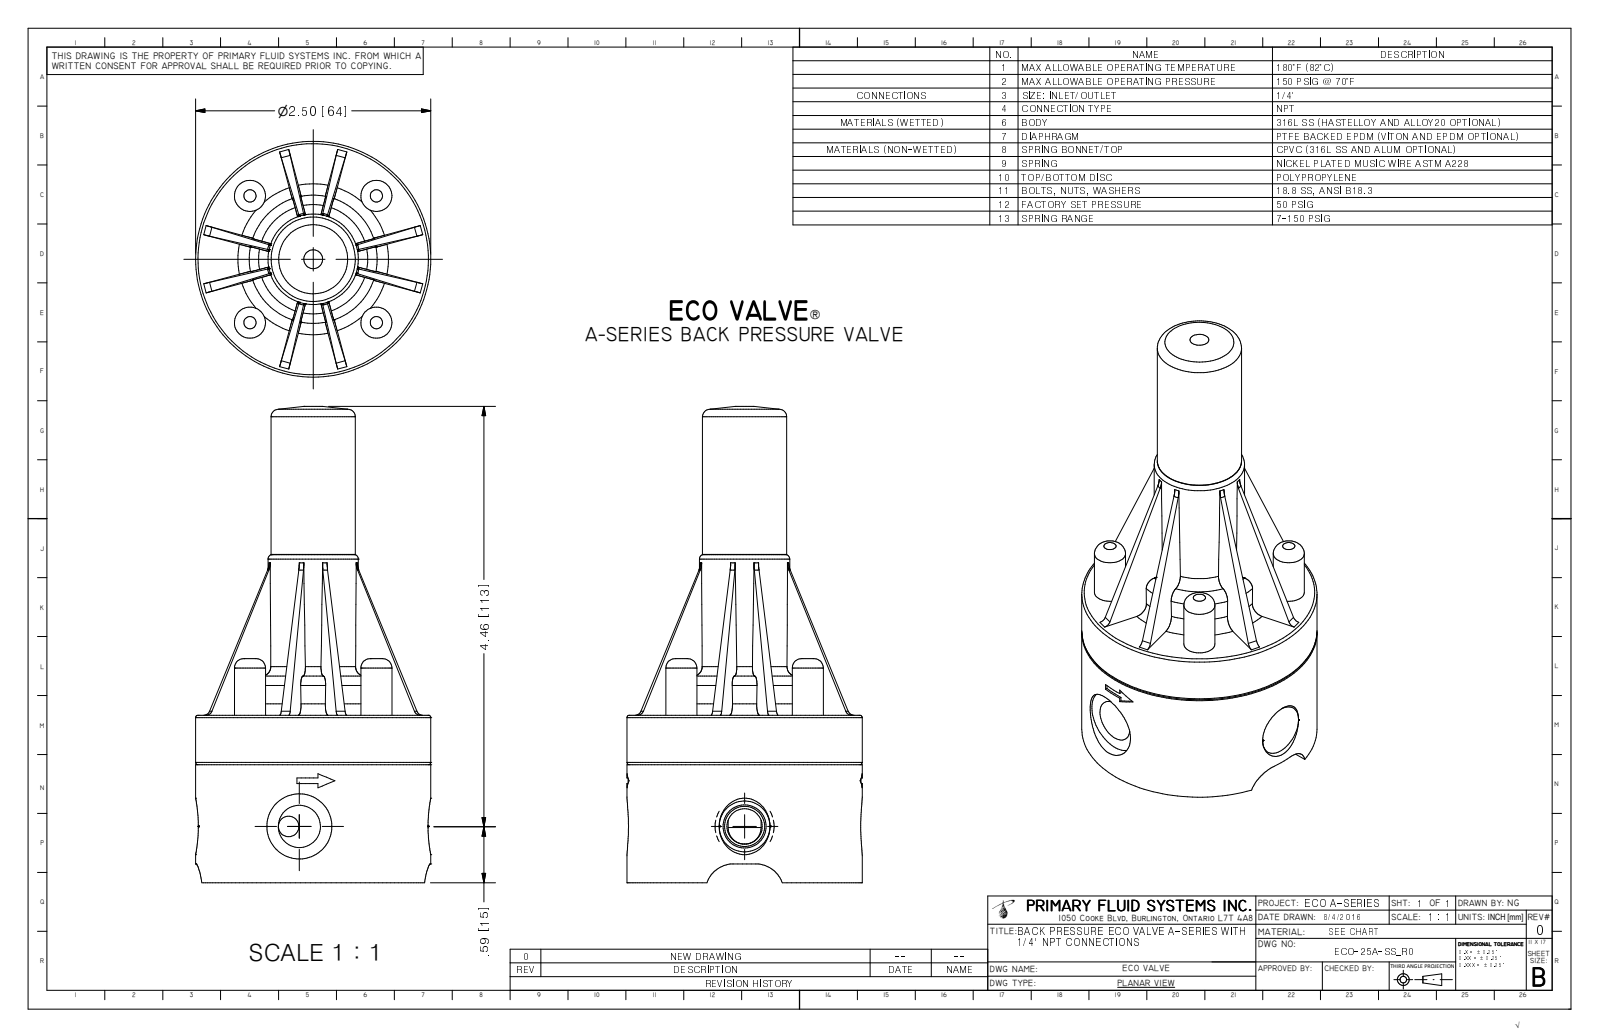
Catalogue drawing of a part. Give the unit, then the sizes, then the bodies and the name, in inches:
Units: inches
Overall size (bounding box): 5.051 × 2.5 × 2.5
Round holes (diameter × count): ⌀0.23 ×4, ⌀0.257 ×4, ⌀0.4 ×4, ⌀0.218 ×1, ⌀0.448 ×1, ⌀0.691 ×1
Round bosses / shafts (diameter × count): ⌀0.33 ×4, ⌀0.256 ×4, ⌀2.5 ×1, ⌀1.36 ×1, ⌀0.96 ×1, ⌀0.895 ×1
Partial cylindrical surfaces — rounded edges, fillets, slot ends (radius × count): R0.07 ×8, R0.128 ×4, R0.3 ×2, R1.23 ×1
Main face-to-face distances: 1.776, 0.2, 1.576, 0.27, 0.05, 0.07, 1.506, 0.275, 0.075, 1.501
Hole centre spacings: 1.344, 1.901, 1.344, 1.344, 0.114, 1.9, 1.902
Volume: 10.89 in³ · Surface area: 55.86 in²
Bodies: 1 solid, 214 faces (99 planar, 52 cylindrical, 63 other)
Part name (STEP PRODUCT): ECO-25A-SS_R0
STEP written by: Autodesk Inventor 2009 (AUTOMOTIVE_DESIGN)
